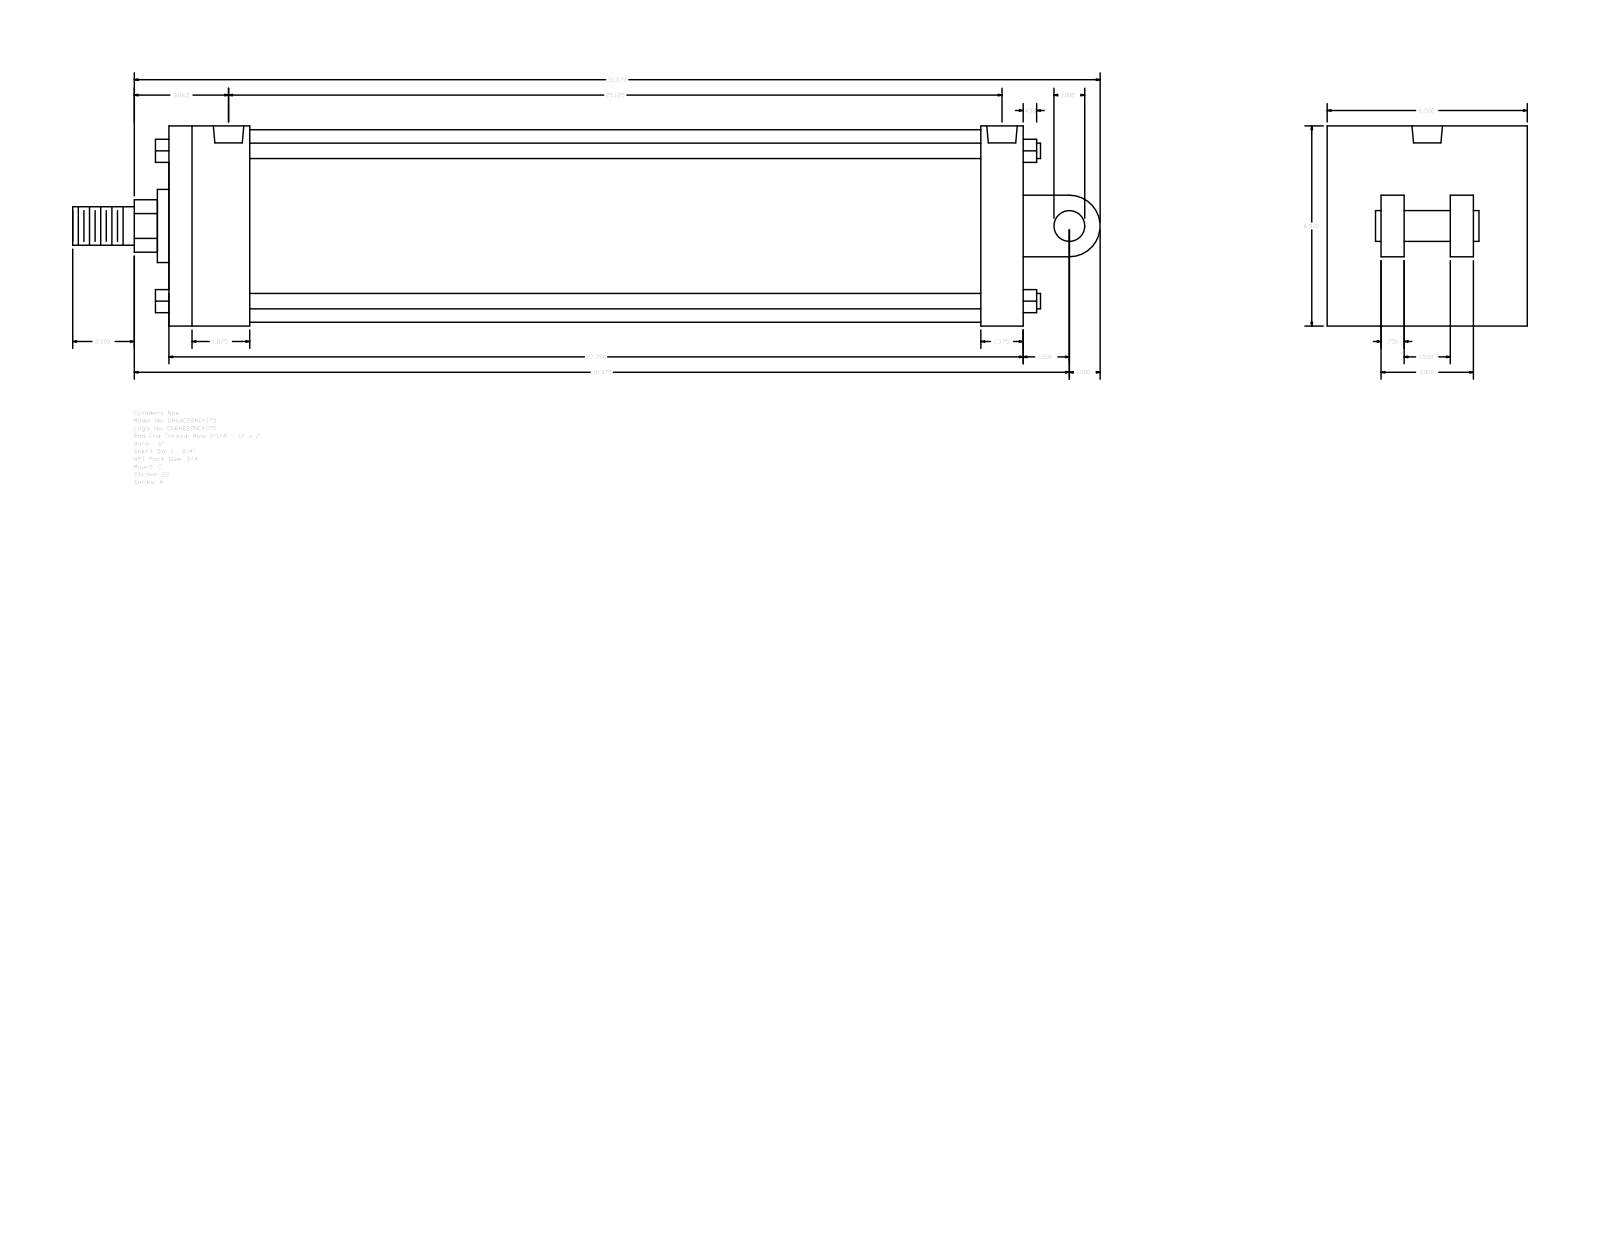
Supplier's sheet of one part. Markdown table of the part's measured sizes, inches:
| quantity | value |
| --- | --- |
| part name | A_C__0600_1.75 |
| STEP written by | GSSL Pune (CONFIG_CONTROL_DESIGN) |
| units | inches |
| bodies | 0 solids, 135 faces (102 planar, 33 cylindrical, 0 other) |
| overall size | 33.375 × 6.5 × 6.5 |
| round holes (diameter × count) | 0.594 × 4, 0.989 × 2 |
| round bosses / shafts (diameter × count) | 0.5 × 4, 6.25 × 1, 2.375 × 1, 1.75 × 1, 1.25 × 1, 1 × 1 |
| partial cylindrical surfaces (radius × count) | 0.852 × 1, 1 × 1 |
| main face-to-face distances | 6.5, 27.75, 0.75, 2.25, 2.625, 25.125, 26.375, 23.75, 1.375, 2.5 |
| hole center spacings | 0.219, 24.687, 24.906, 25.125 |
